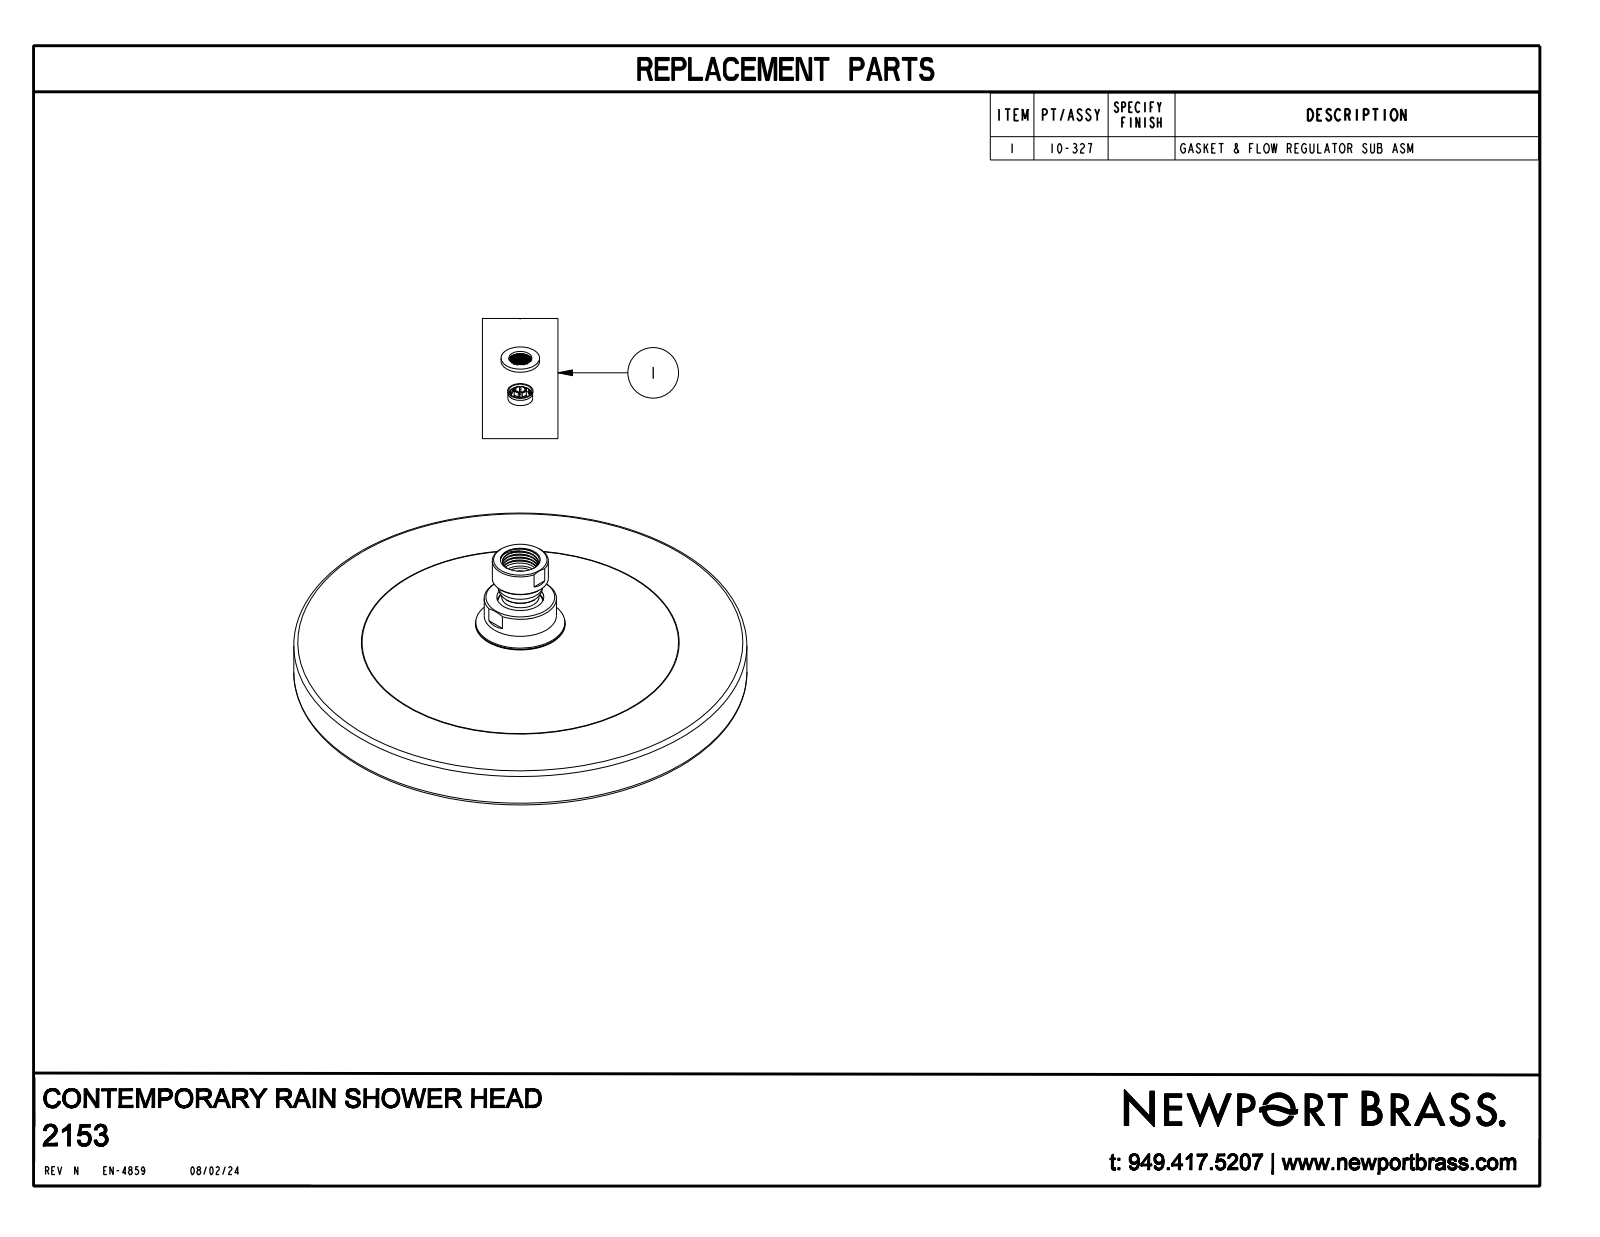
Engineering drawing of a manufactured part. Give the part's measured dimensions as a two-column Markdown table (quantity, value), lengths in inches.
| quantity | value |
| --- | --- |
| part name | 2153 |
| STEP written by | CREO PARAMETRIC BY PTC INC, 2018400 (AUTOMOTIVE_DESIGN) |
| units | inches |
| bodies | 2 solids, 698 faces (198 planar, 112 cylindrical, 388 other) |
| overall size | 8.9 × 8.9 × 2.959 |
| volume | 59.09 in³ |
| surface area | 165.8 in² |
| round holes (diameter × count) | 0.18 × 54, 0.92 × 1, 1.01 × 1, 1.142 × 1 |
| round bosses / shafts (diameter × count) | 8.9 × 1, 1.75 × 1, 1.42 × 1, 1.1 × 1, 0.875 × 1 |
| partial cylindrical surfaces (radius × count) | 0.09 × 6 |
| main face-to-face distances | 0.83, 0.033, 0.798, 1.272, 1.239, 0.441, 1.28, 1.247, 0.449, 2.816 |
| hole center spacings | 0.996, 1.925, 2.723, 3.335, 3.719, 2.555, 2.247, 0.887 |
